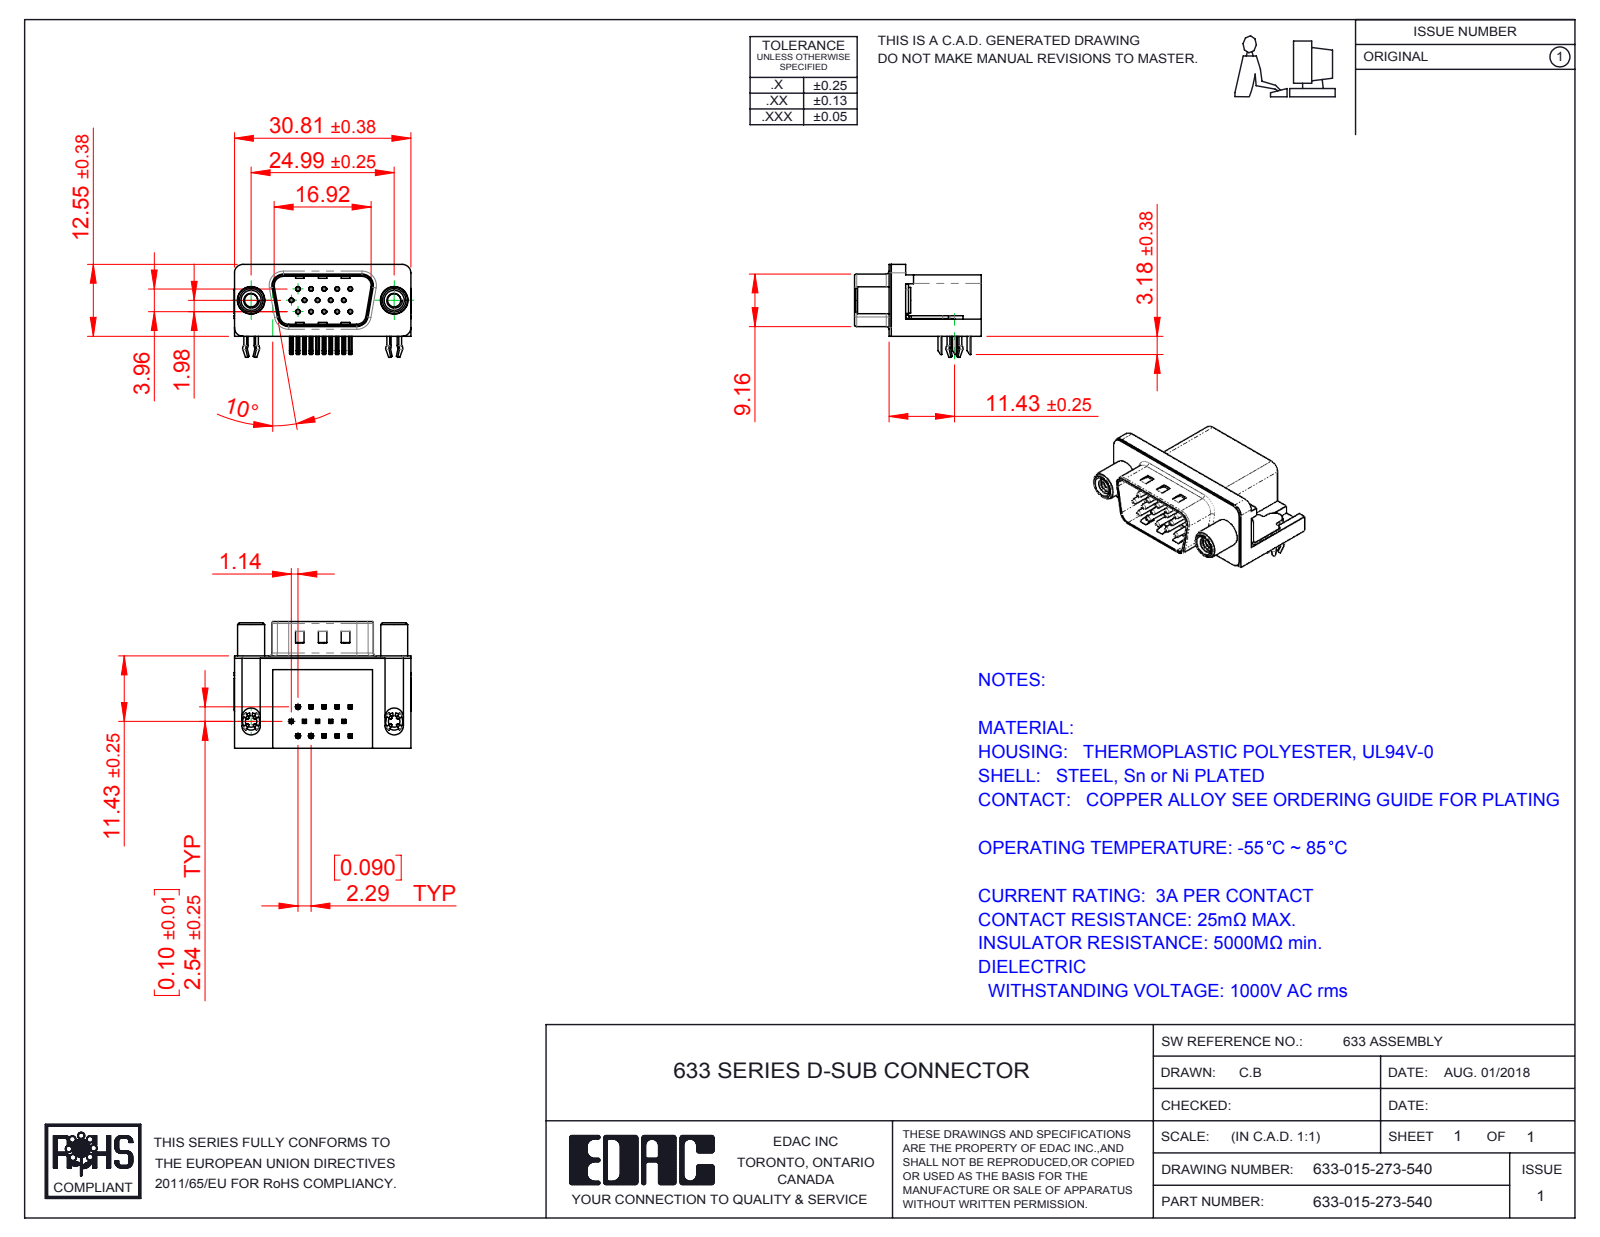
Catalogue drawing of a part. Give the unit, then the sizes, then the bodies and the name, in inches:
Units: inches
Overall size (bounding box): 1.216 × 0.87 × 0.64
Round holes (diameter × count): ⌀0.014 ×15, ⌀0.031 ×15, ⌀0.079 ×2, ⌀0.091 ×2, ⌀0.122 ×2, ⌀0.157 ×2, ⌀0.189 ×2, ⌀0.197 ×2
Round bosses / shafts (diameter × count): ⌀0.03 ×15, ⌀0.193 ×2, ⌀0.185 ×2, ⌀0.177 ×2, ⌀0.152 ×2, ⌀0.118 ×2
Partial cylindrical surfaces — rounded edges, fillets, slot ends (radius × count): R0.01 ×64, R0.005 ×30, R0.039 ×16, R0.02 ×9, R0.063 ×8, R0.059 ×7, R0.035 ×4, R0.079 ×4
Main face-to-face distances: 0.016, 0.407, 0.618, 0.114, 0.264, 0.098, 0.634, 0.014, 0.421, 0.52
Hole centre spacings: 0.156, 0.09, 0.18, 0.09, 0.238, 0.27, 0.312, 0.238
Volume: 0.255 in³ · Surface area: 8.827 in²
Bodies: 21 solids, 1557 faces (895 planar, 457 cylindrical, 205 other)
Part name (STEP PRODUCT): 633 Housing_15 Contact; 633-015-273-540; 633 Round Threaded Standoff; 633 4 Prong Board Lock (+5 more)
STEP written by: SolidWorks 2016 (CONFIG_CONTROL_DESIGN)
